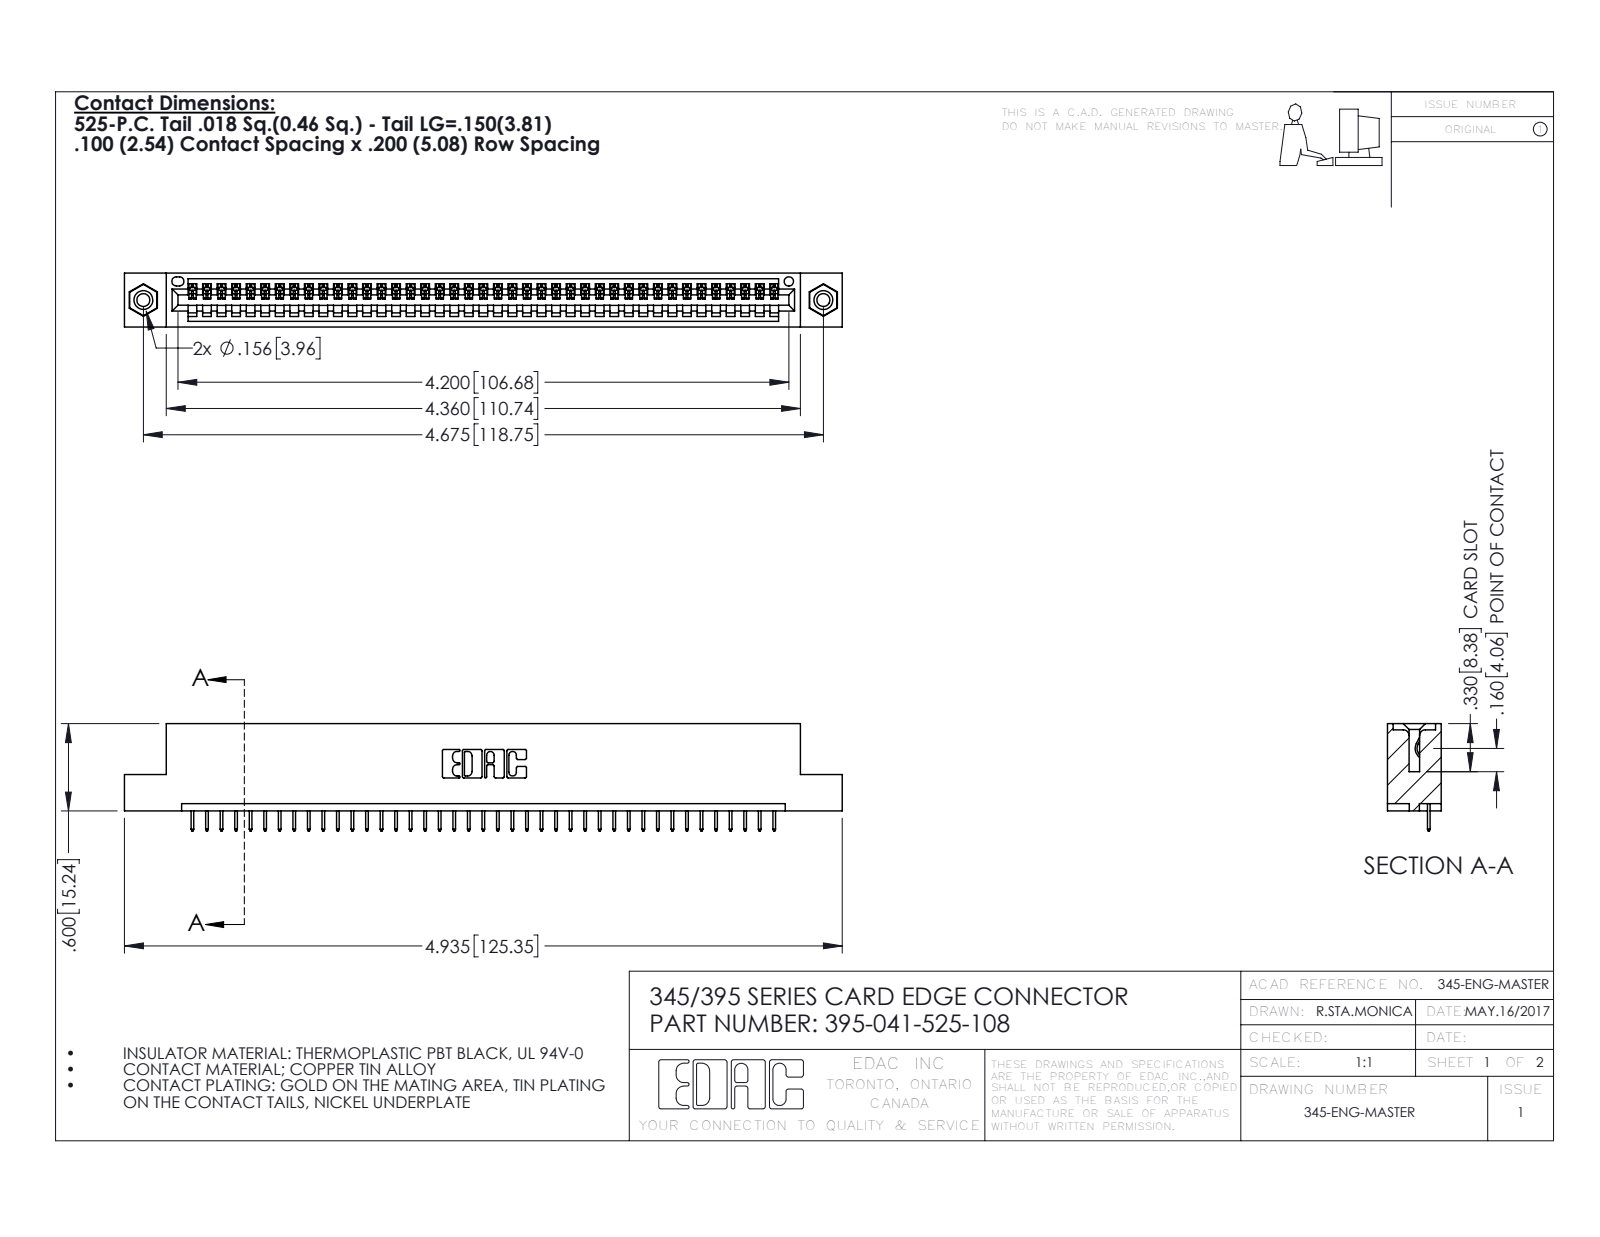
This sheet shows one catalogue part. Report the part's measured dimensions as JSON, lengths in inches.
{"part_name": "345-292-001_345-293-125; 345-250-001_345-250-003-102; 345 Part_Flush Mounting Lugs - 0.156 Dia-TI; 395-041-525-108", "step_written_by": "SolidWorks 2020 (CONFIG_CONTROL_DESIGN)", "units": "inches", "bodies": {"solids": 44, "faces": 2728, "planar": 1998, "cylindrical": 714, "other": 16}, "overall_size": [4.935, 0.737, 0.37], "volume_in3": 0.715, "surface_area_in2": 23.29, "round_holes": [[0.089, 2], [0.125, 2], [0.156, 2], [0.064, 1]], "round_bosses_or_shafts": [[0.155, 2]], "partial_cylinders_radius": [[0.006, 82], [0.01, 22], [0.007, 6], [0.031, 6], [0.026, 3], [0.031, 2], [0.04, 2], [0.014, 1]], "face_to_face_distances": [0.072, 0.298, 0.37, 0.2, 0.098, 0.272, 0.025, 0.225, 0.072, 0.149], "hole_center_spacings": [0.27, 4.439, 4.675]}
